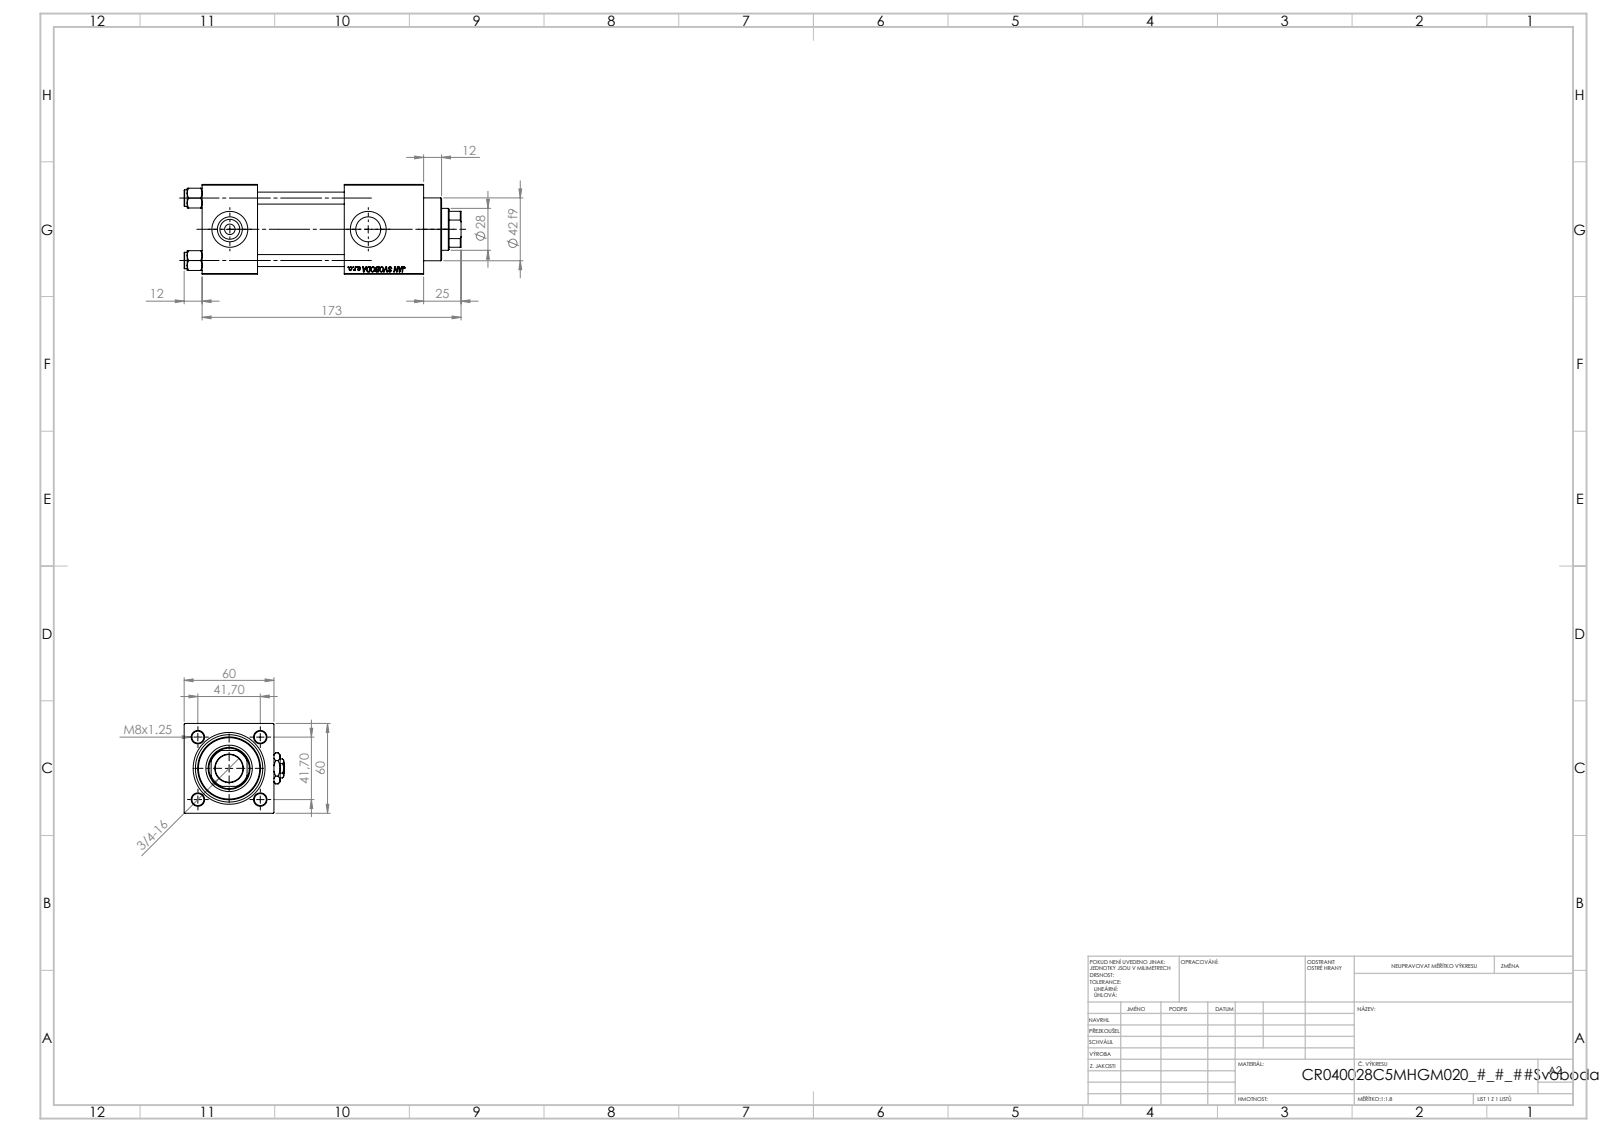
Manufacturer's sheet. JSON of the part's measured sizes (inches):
{"part_name": "NUT_M5_C; V215CR_C_Body; V215CR_C_TYCINKA; V215CR_VCP_C (+2 more)", "step_written_by": "SolidWorks 2019 (CONFIG_CONTROL_DESIGN)", "units": "inches", "bodies": {"solids": 12, "faces": 1202, "planar": 550, "cylindrical": 94, "other": 558}, "overall_size": [7.283, 2.638, 2.362], "volume_in3": 25.8, "surface_area_in2": 175.3, "round_holes": [[0.315, 4], [0.276, 2], [0.656, 2], [0.945, 2], [0.728, 1], [1.102, 1], [1.22, 1], [1.575, 1], [1.772, 1]], "round_bosses_or_shafts": [[0.433, 4], [1.811, 1], [1.654, 1]], "partial_cylinders_radius": [[0.531, 1]], "face_to_face_distances": [2.362, 1.457, 2.283, 3.74, 2.087, 4.697, 3.24, 0.957, 5.827, 4.37], "hole_center_spacings": [1.161, 1.642, 2.322, 3.642]}
